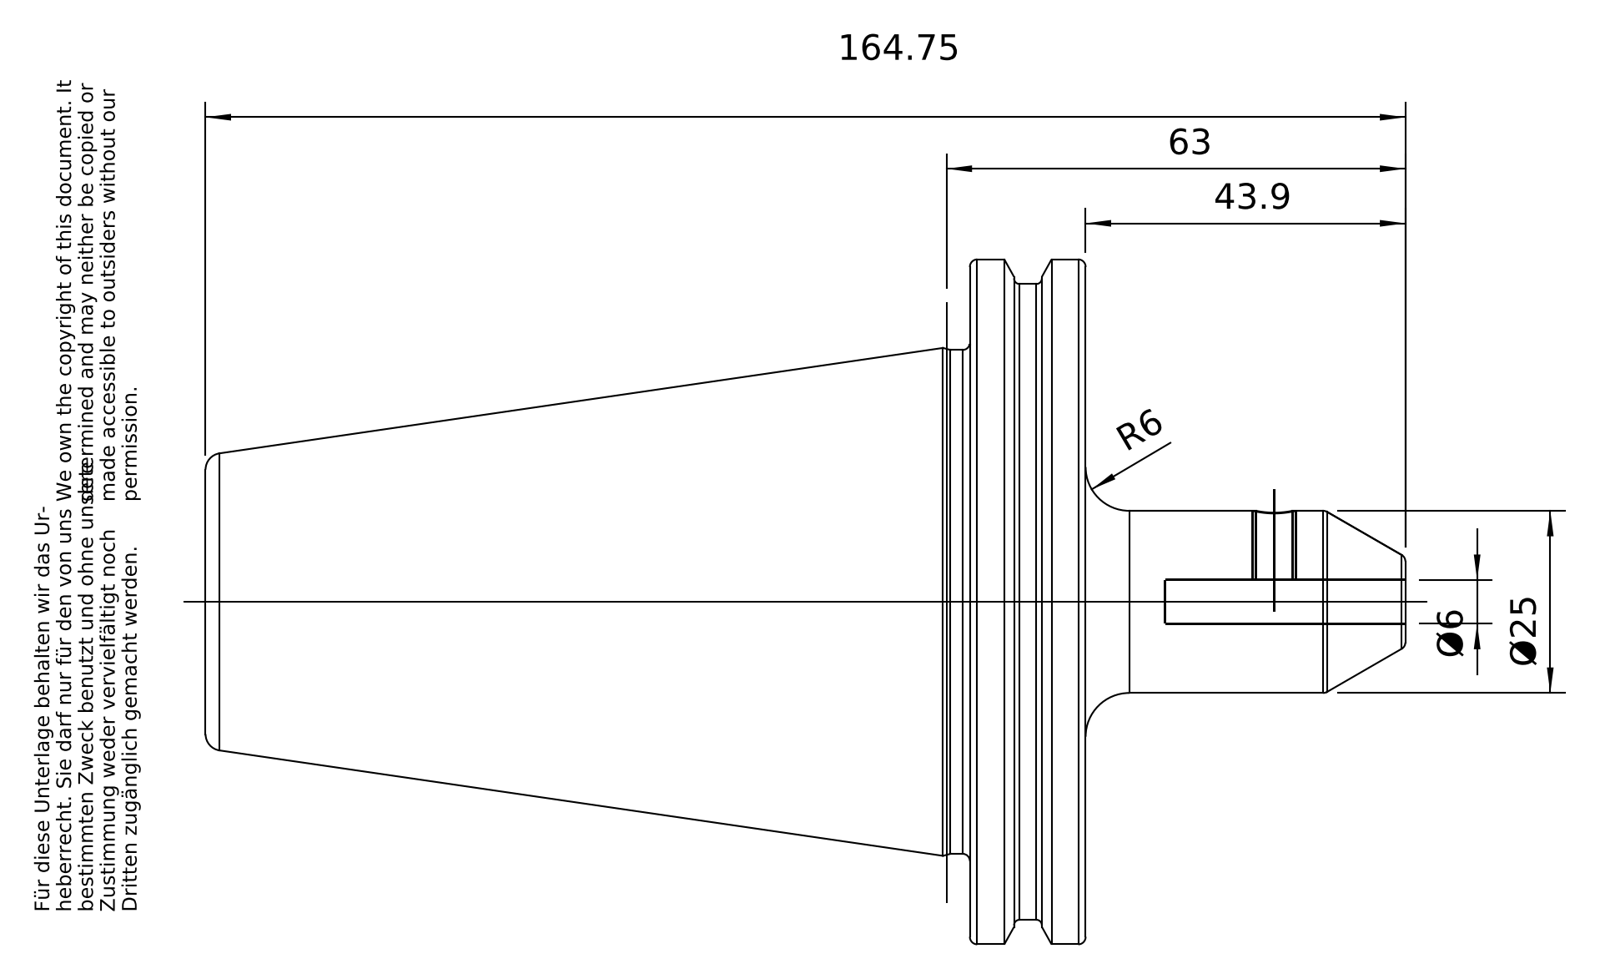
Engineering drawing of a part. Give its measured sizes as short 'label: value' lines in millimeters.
name: 50-300-06
written by: PRO/ENGINEER BY PARAMETRIC TECHNOLOGY CORPORATION, 2010430 (CONFIG_CONTROL_DESIGN)
unit: mm
bodies: 1 solid, 103 faces (21 planar, 32 cylindrical, 50 other)
size: 164.6 × 97.47 × 94
volume: 358 216 mm³; area: 46 302 mm²
holes: 2× ⌀6, 1× ⌀5, 1× ⌀20.75, 1× ⌀25.01, 1× ⌀25.7
bosses: 1× ⌀91, 1× ⌀69.15, 1× ⌀25, 1× ⌀24.01
rounds: 5× R1.75, 1× R48.74
face distances: 15.85, 104.8, 120.65, 72.8, 25.8, 48, 56.8, 72.65, 7.65, 65.15
